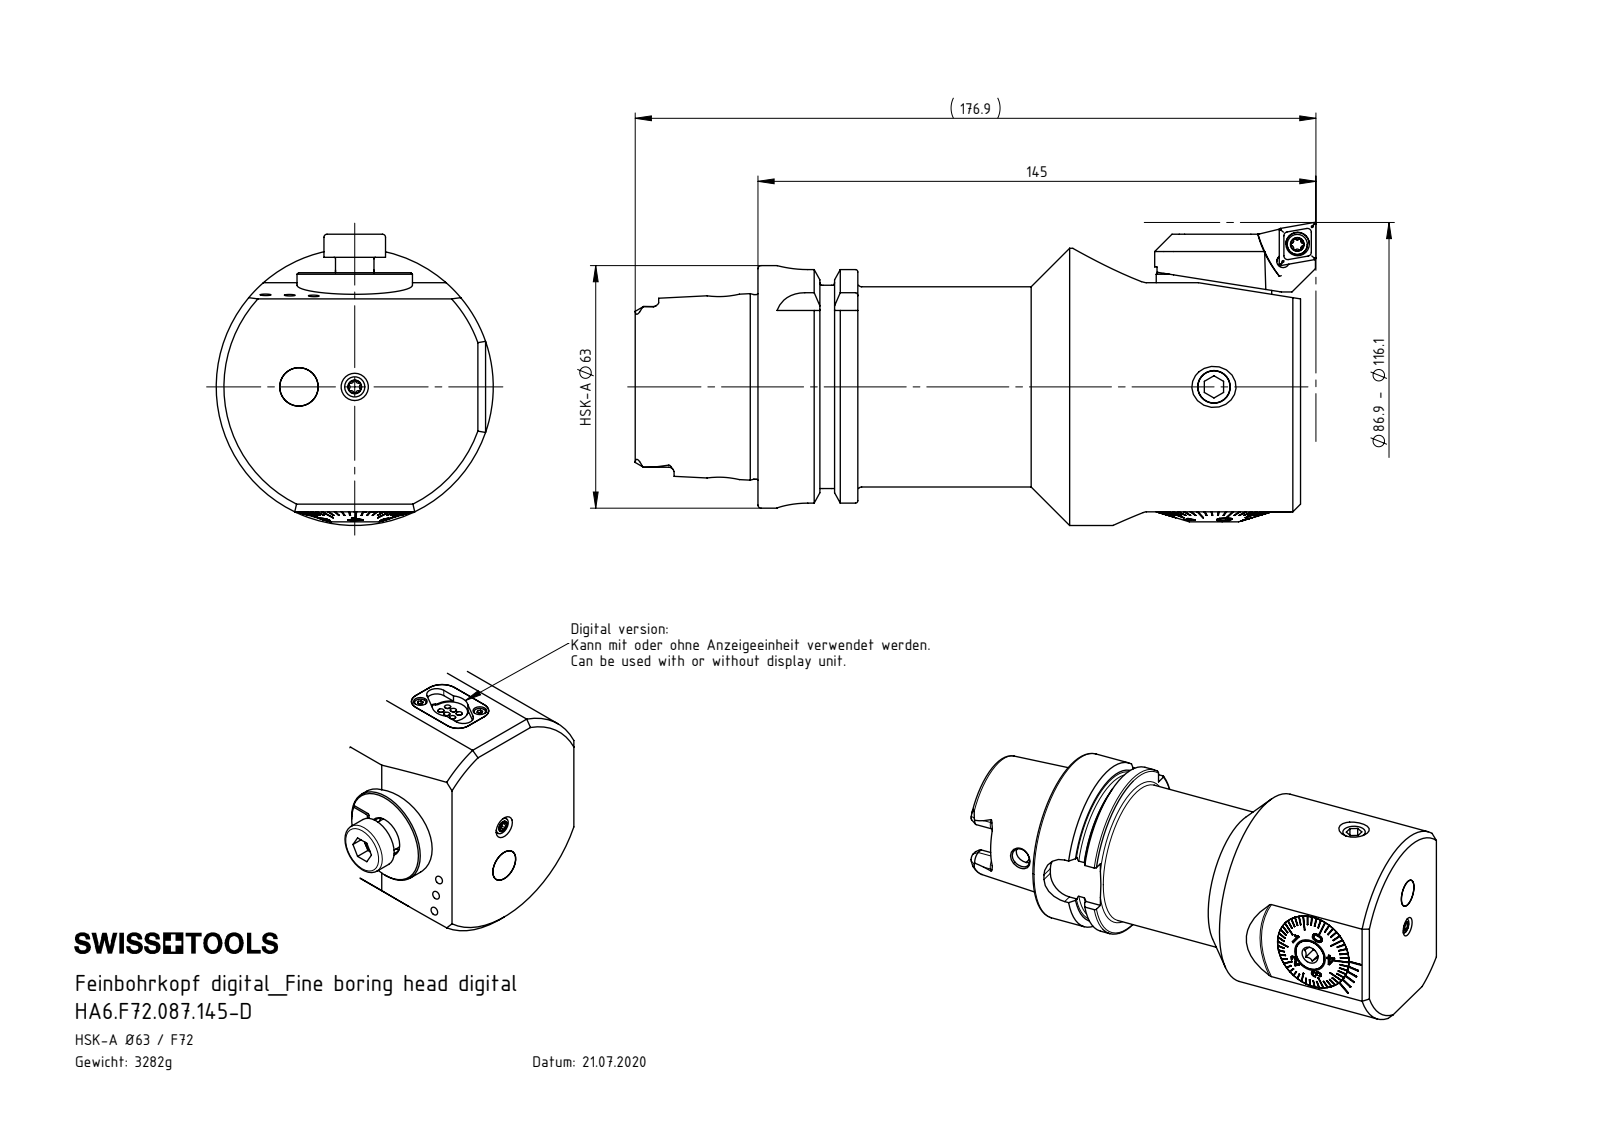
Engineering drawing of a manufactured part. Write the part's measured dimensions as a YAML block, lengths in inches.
part_name: "DIN 3771 - 25x1.5; PEF-DA3.010.032_A_F72; DIN 7984 - M10 x 16; DIN 3771 - 13x1 (+8 more)"
step_written_by: "SolidWorks 2022 (CONFIG_CONTROL_DESIGN)"
units: inches
bodies: {solids: 31, faces: 1123, planar: 510, cylindrical: 253, other: 360}
overall_size: [6.807, 2.979, 2.835]
volume: 25.68
surface_area: 122.1
round_holes:
  - {diameter: 0.165, count: 5}
  - {diameter: 0.098, count: 3}
  - {diameter: 0.335, count: 3}
  - {diameter: 0.063, count: 2}
  - {diameter: 0.087, count: 2}
  - {diameter: 0.13, count: 2}
  - {diameter: 0.394, count: 2}
  - {diameter: 0.512, count: 2}
  - {diameter: 0.197, count: 1}
  - {diameter: 0.295, count: 1}
  - {diameter: 0.315, count: 1}
  - {diameter: 0.374, count: 1}
round_bosses_or_shafts:
  - {diameter: 0.075, count: 6}
  - {diameter: 0.394, count: 2}
  - {diameter: 0.15, count: 2}
  - {diameter: 0.079, count: 2}
  - {diameter: 2.835, count: 1}
  - {diameter: 2.48, count: 1}
  - {diameter: 2.163, count: 1}
  - {diameter: 2.047, count: 1}
partial_cylinders:
  - {radius: 0.013, count: 6}
  - {radius: 0.023, count: 6}
  - {radius: 0.043, count: 6}
  - {radius: 0.047, count: 6}
  - {radius: 0.055, count: 6}
  - {radius: 0.079, count: 6}
  - {radius: 0.098, count: 6}
  - {radius: 0.113, count: 4}
face_to_face_distances: [5.551, 0.63, 2.087, 0.102, 1.022, 4.53, 2.445, 2.343, 0.256, 0.209]
hole_center_spacings: [0.375, 0.048, 0.334, 0.417, 0.571, 0.707, 0.75, 0.78]
